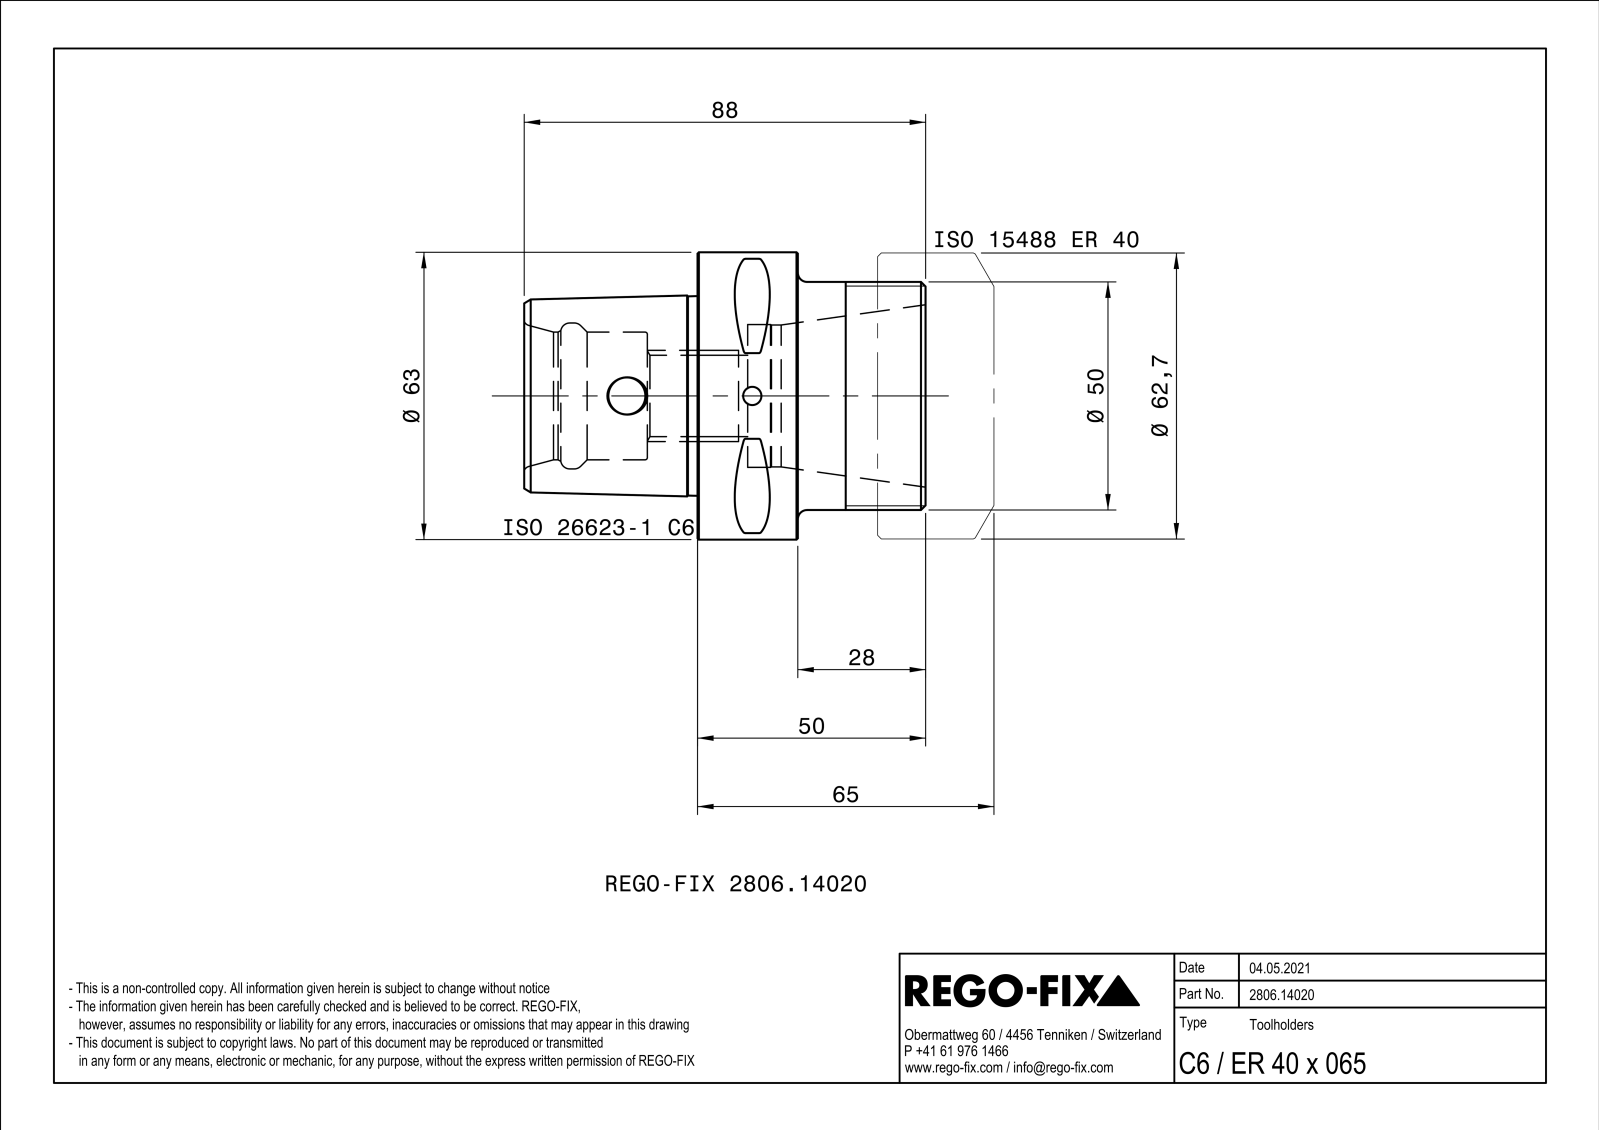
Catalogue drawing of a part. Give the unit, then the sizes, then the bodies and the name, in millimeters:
Units: millimetres
Overall size (bounding box): 88 × 63 × 63
Round holes (diameter × count): ⌀4 ×1, ⌀8.1 ×1, ⌀17.84 ×1, ⌀28 ×1, ⌀31.1 ×1, ⌀31.3 ×1, ⌀32 ×1
Round bosses / shafts (diameter × count): ⌀63 ×1, ⌀50 ×1
Partial cylindrical surfaces — rounded edges, fillets, slot ends (radius × count): R0.5 ×8, R5 ×1
Main face-to-face distances: 11, 22, 28, 39, 50, 88, 60, 49, 38, 24.89
Hole centre spacings: 27.5
Volume: 115 183 mm³ · Surface area: 27 147 mm²
Bodies: 1 solid, 108 faces (21 planar, 22 cylindrical, 65 other)
Part name (STEP PRODUCT): NOCUT
STEP written by: SIEMENS PLM Software Solid Edge ST10 (AUTOMOTIVE_DESIGN)
